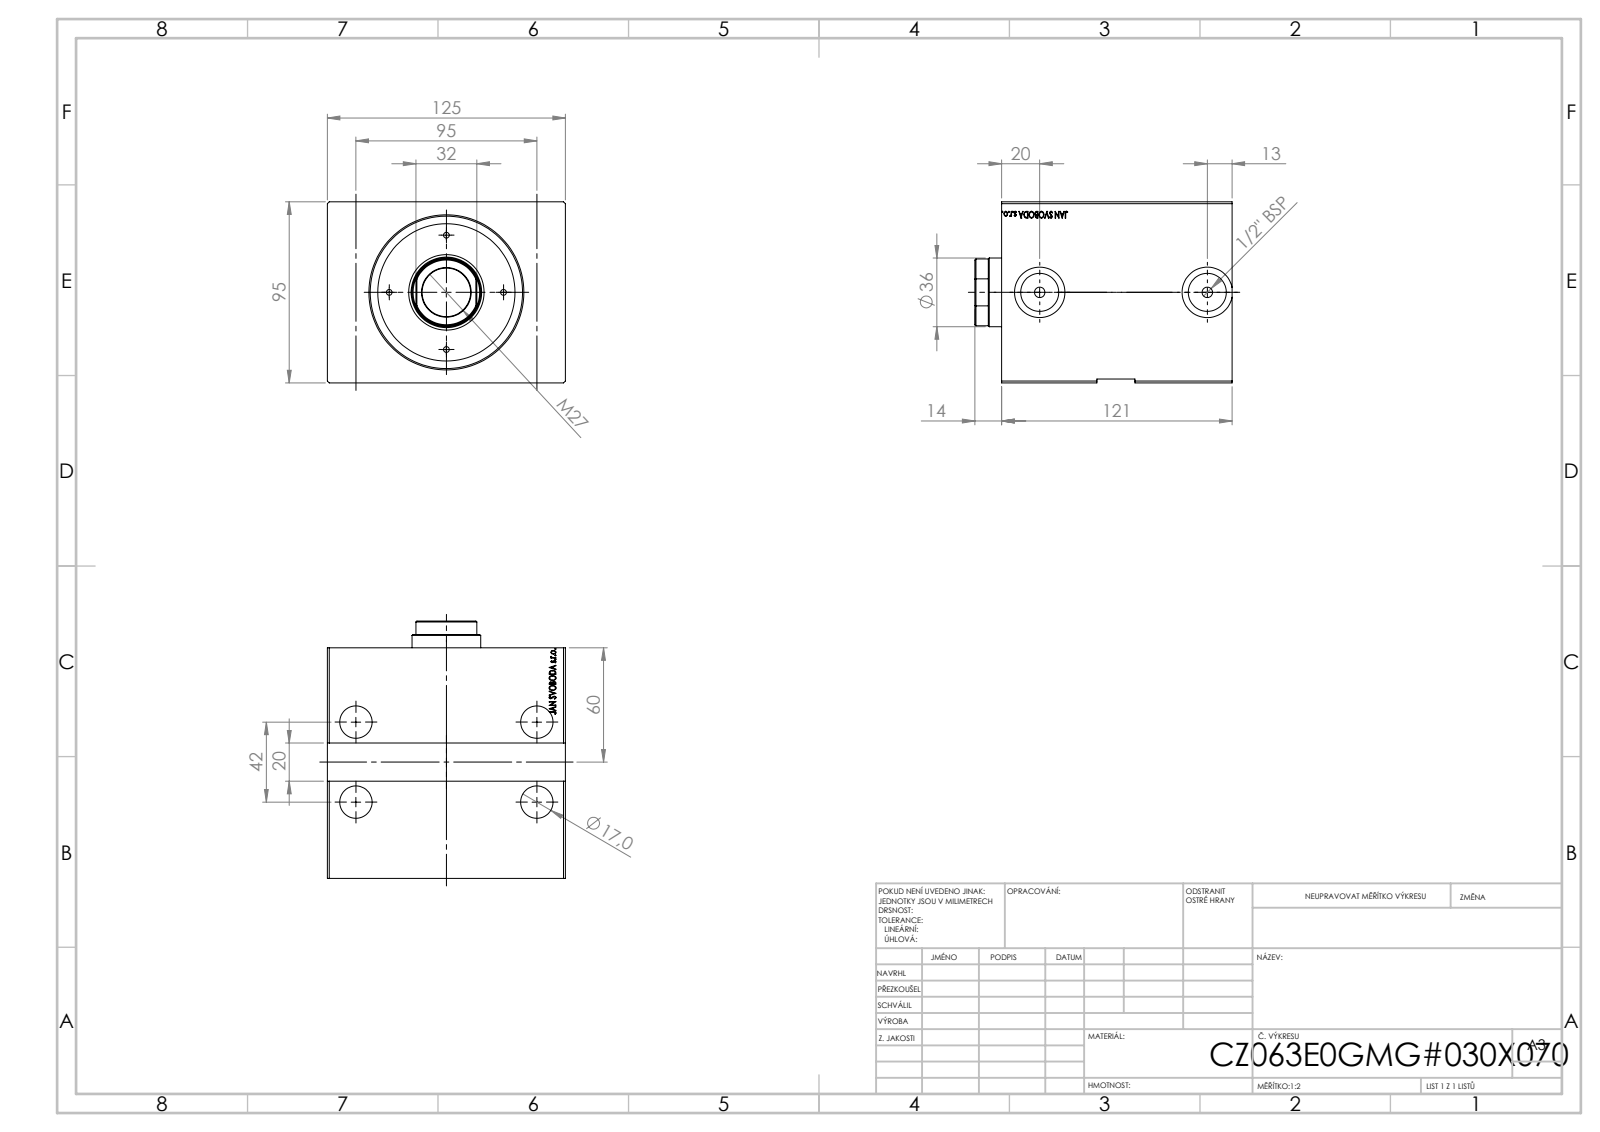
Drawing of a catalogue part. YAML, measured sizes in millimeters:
step_written_by: "SolidWorks 2019 (CONFIG_CONTROL_DESIGN)"
units: millimeters
bodies: {solids: 1, faces: 794, planar: 387, cylindrical: 25, other: 382}
overall_size: [125, 121, 95]
volume: 843463
surface_area: 121713
round_holes:
  - {diameter: 17, count: 4}
  - {diameter: 5.5, count: 2}
  - {diameter: 20, count: 2}
  - {diameter: 26.5, count: 2}
  - {diameter: 36, count: 1}
  - {diameter: 63, count: 1}
  - {diameter: 80, count: 1}
face_to_face_distances: [95, 125, 121, 102.5, 18.5, 2, 93, 91, 11.5, 30]
hole_center_spacings: [42, 95, 103.87, 88]
